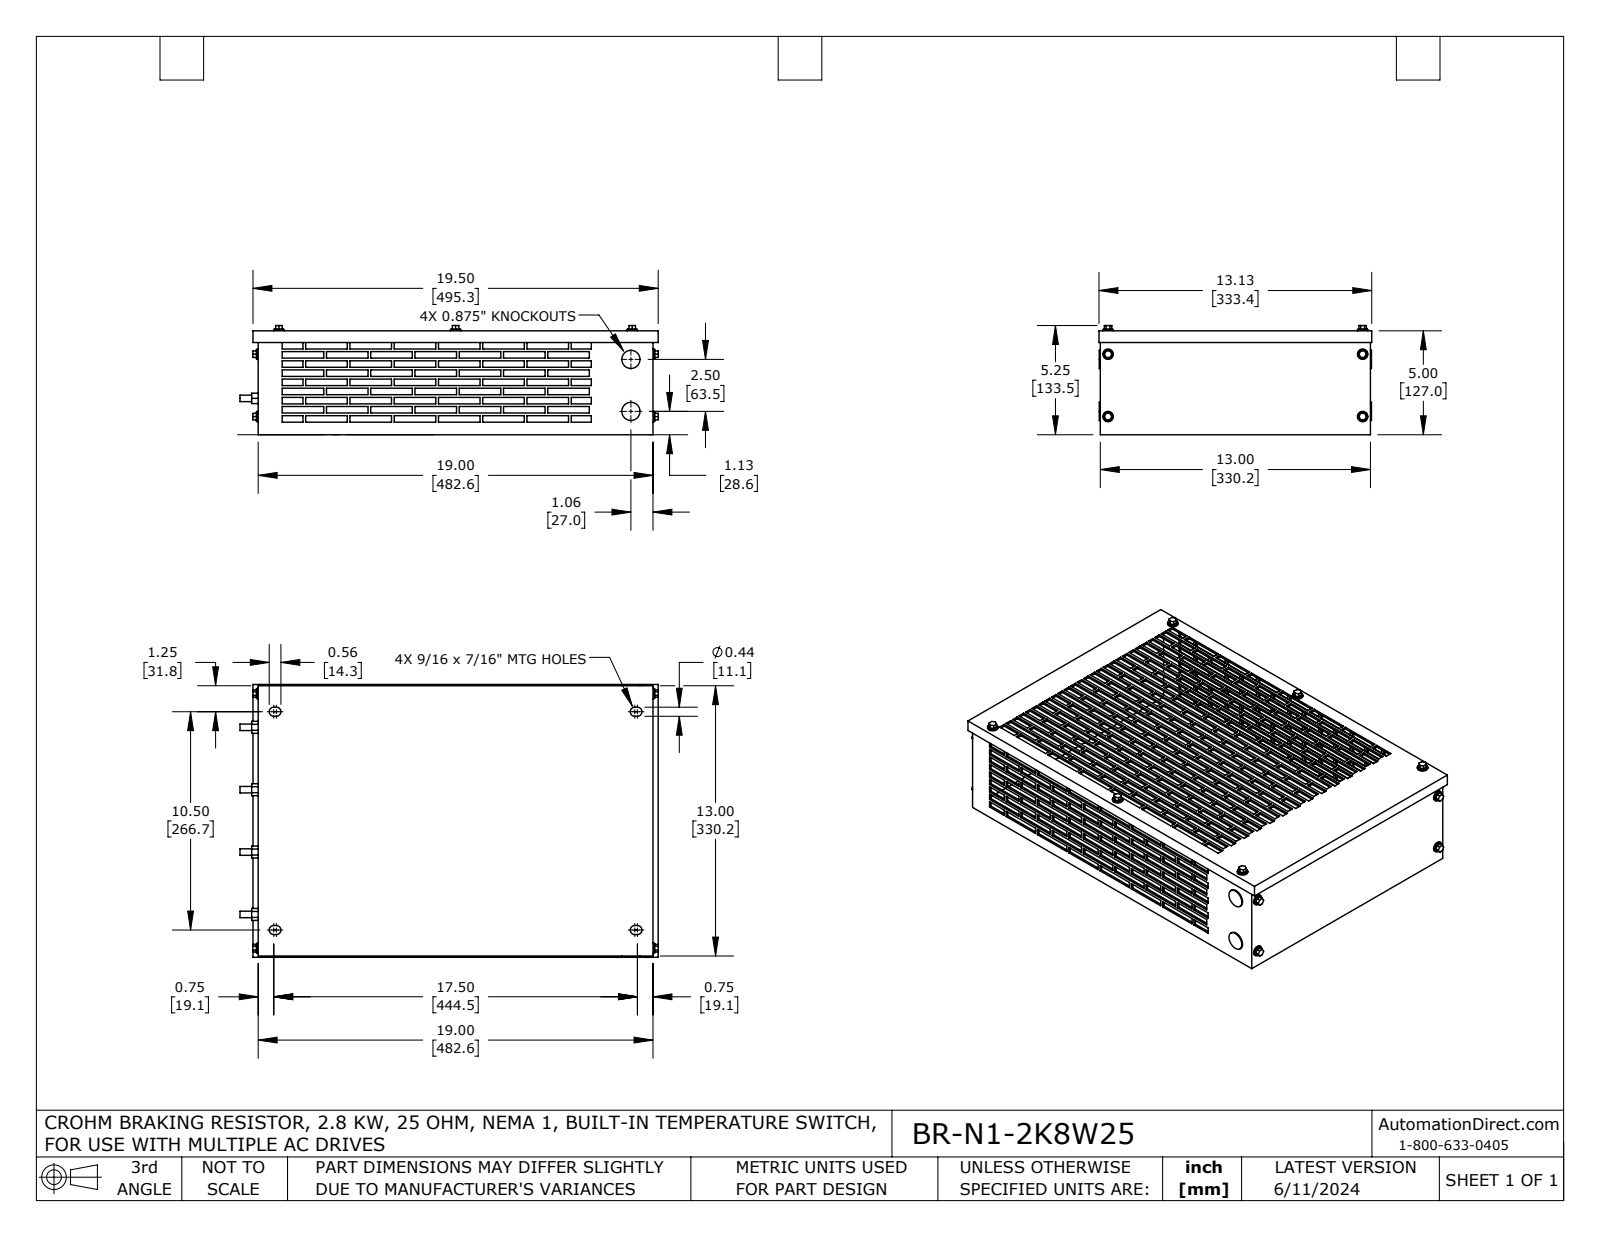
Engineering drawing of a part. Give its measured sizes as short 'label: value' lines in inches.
name: BR-N1-2K8W25
written by: SolidWorks 2021 (AUTOMOTIVE_DESIGN)
unit: in
bodies: 37 solids, 1688 faces (1572 planar, 116 cylindrical, 0 other)
size: 20.129 × 13.125 × 5.254
volume: 62.81 in³; area: 1 412 in²
holes: 10× ⌀0.25, 2× ⌀0.75
bosses: 10× ⌀0.5, 10× ⌀0.437, 4× ⌀0.313, 2× ⌀0.875
rounds: 8× R0.219
face distances: 0.1, 4.9, 5, 4.8, 18.9, 12.9, 19, 18.8, 13, 12.8
hole spacings: 12.25, 8.5, 14.91, 3, 12.611, 17, 20.954, 2.5
